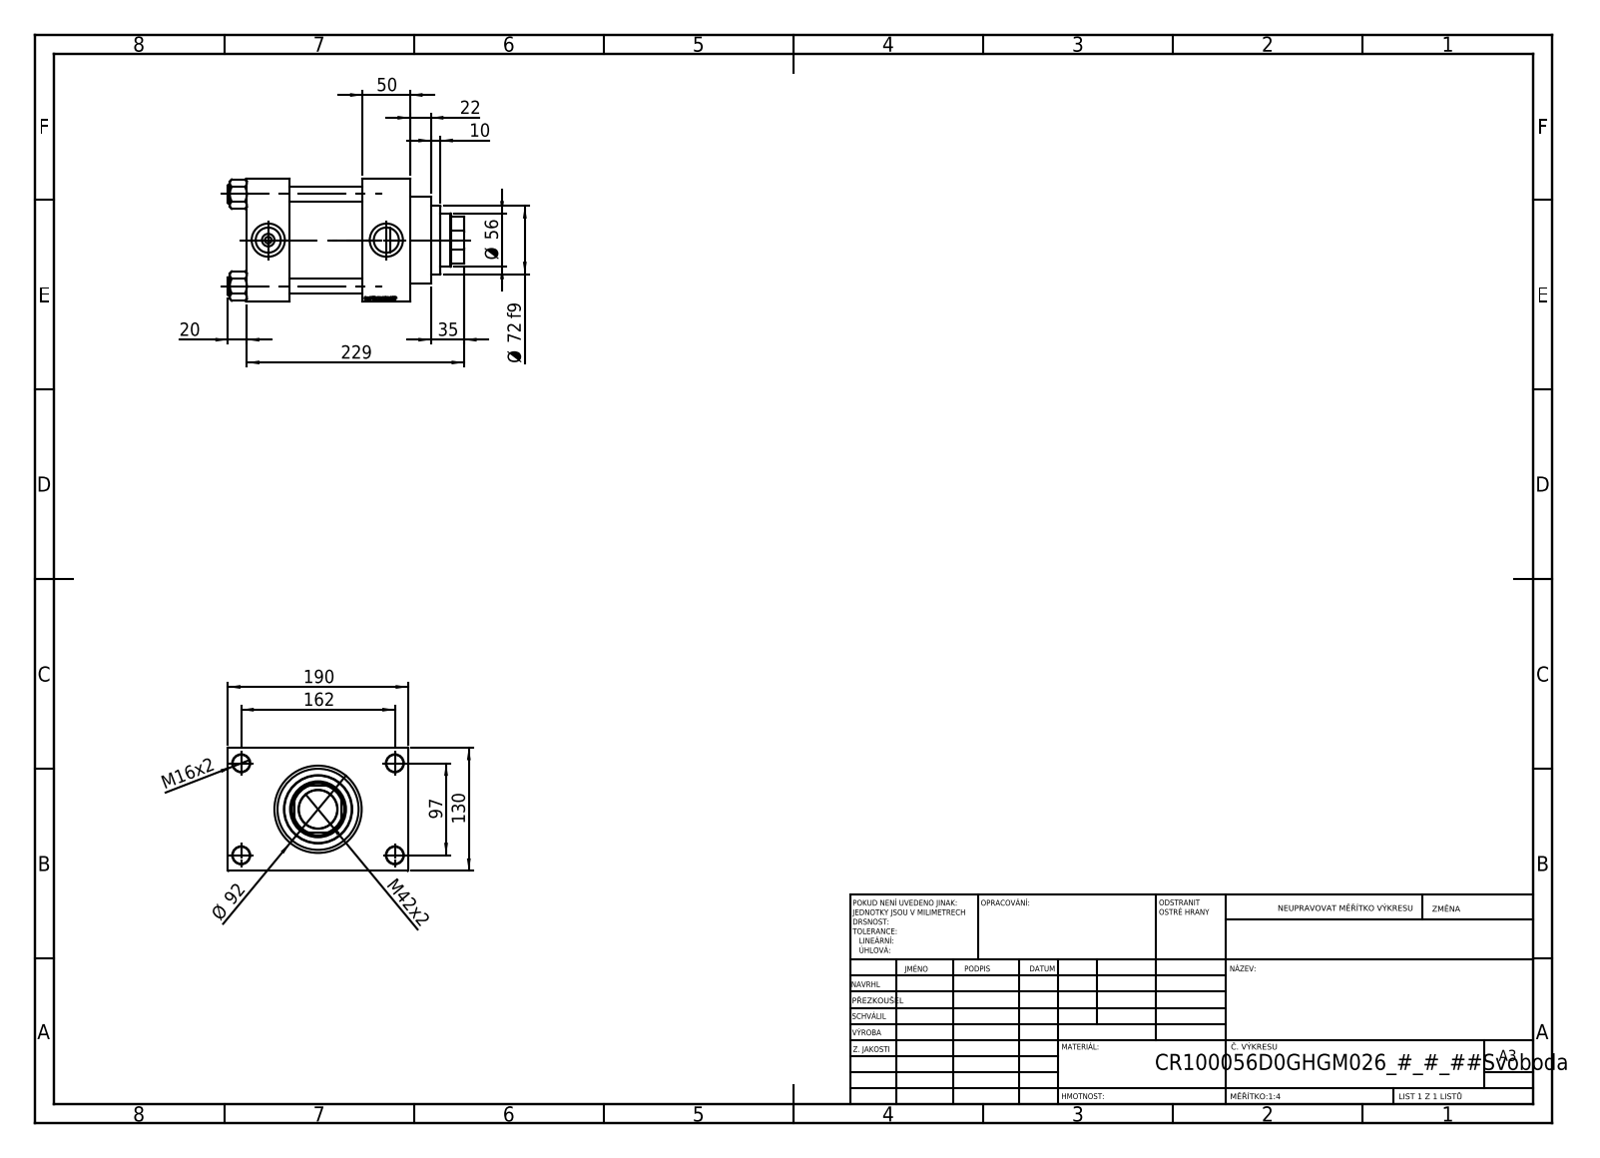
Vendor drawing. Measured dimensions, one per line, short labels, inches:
name: NUT_M5_D; V215CR_D_TYCINKA; V215_VC_A; V215CR_D_Body (+1 more)
written by: SolidWorks 2019 (CONFIG_CONTROL_DESIGN)
unit: in
bodies: 11 solids, 1151 faces (545 planar, 88 cylindrical, 518 other)
size: 9.803 × 7.48 × 5.118
volume: 161.9 in³; area: 571.2 in²
holes: 4× ⌀0.63, 4× ⌀0.709, 2× ⌀0.276, 2× ⌀1.041, 2× ⌀1.378, 1× ⌀1.594, 1× ⌀2.205, 1× ⌀2.323, 1× ⌀2.992, 1× ⌀3.366, 1× ⌀3.937
bosses: 4× ⌀0.748, 1× ⌀4.173, 1× ⌀3.622, 1× ⌀2.835
rounds: 1× R1.063
face distances: 5.118, 1.969, 1.772, 4.803, 3.031, 5, 6.772, 1.181, 6.299, 7.48
hole spacings: 1.281, 2.698, 3.717, 3.815, 4.026, 5.096, 6.367, 3.819
